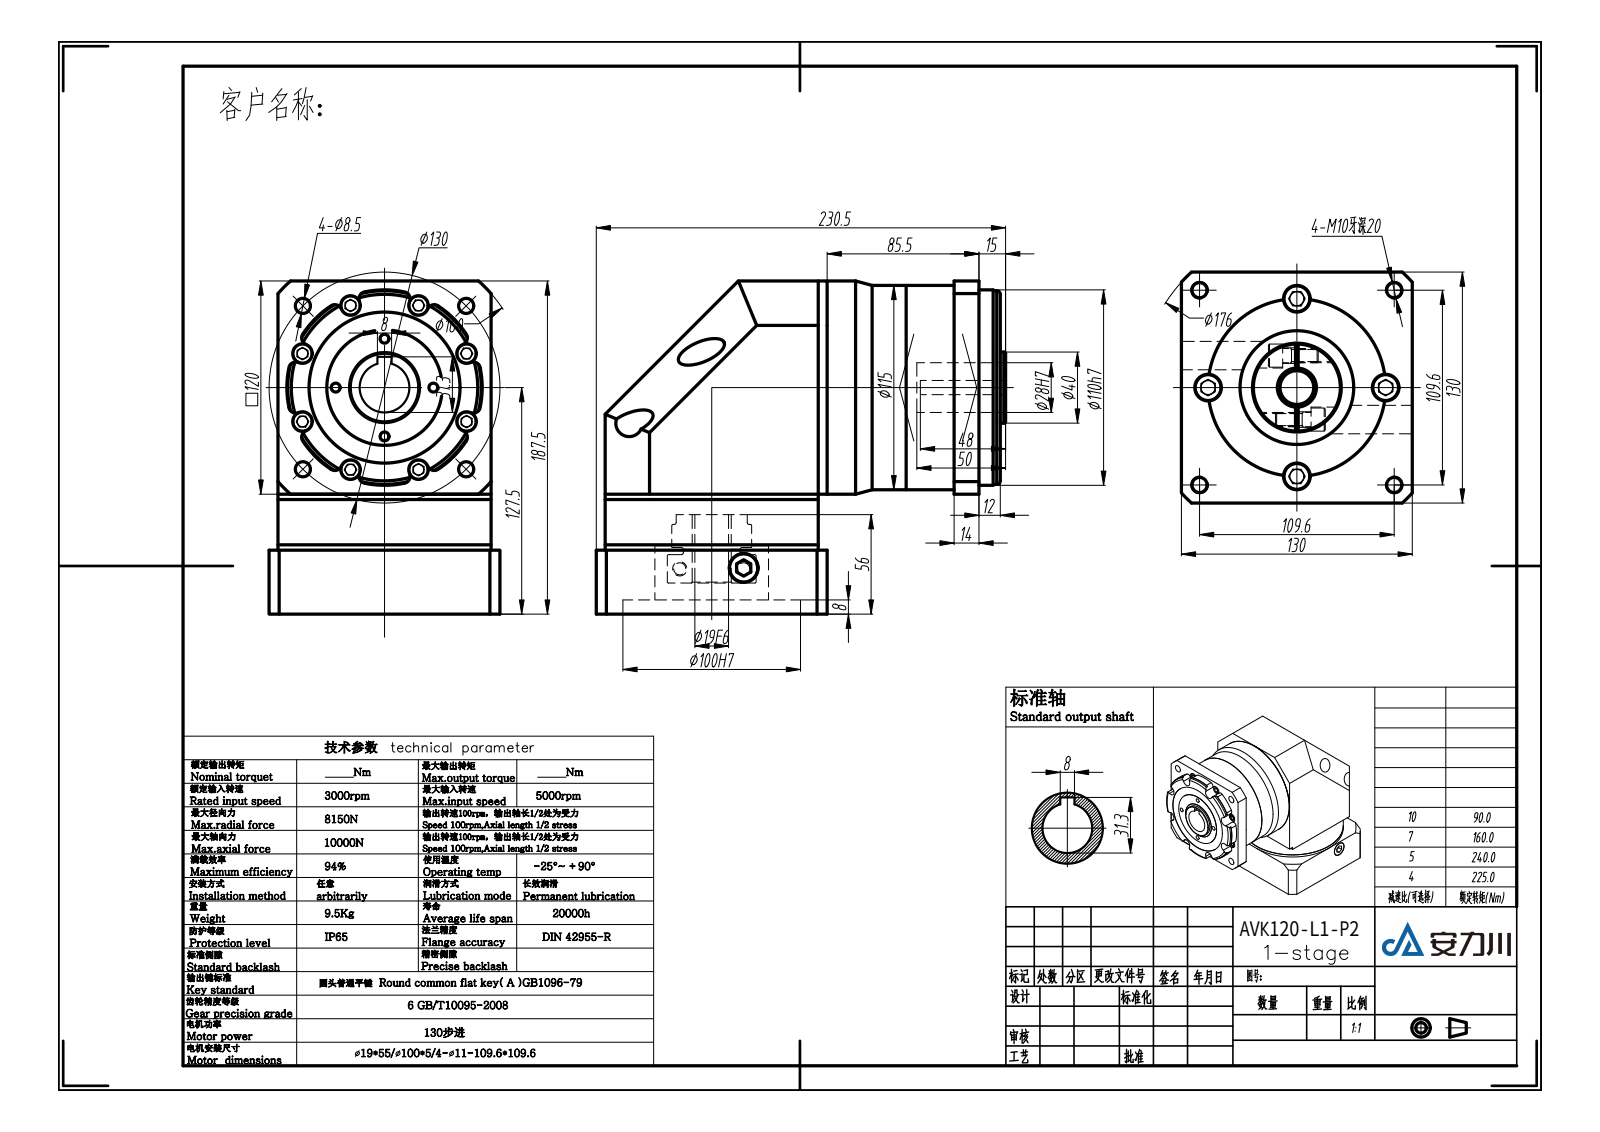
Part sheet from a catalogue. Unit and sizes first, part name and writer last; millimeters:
Units: millimetres
Overall size (bounding box): 230.5 × 187.5 × 130
Round holes (diameter × count): ⌀15 ×10, ⌀8.5 ×8, ⌀11 ×8, ⌀5 ×4, ⌀16 ×2, ⌀19 ×1, ⌀20 ×1, ⌀22 ×1, ⌀28 ×1, ⌀45.2 ×1, ⌀70 ×1, ⌀85 ×1
Round bosses / shafts (diameter × count): ⌀13 ×10, ⌀9.5 ×8, ⌀120 ×2, ⌀15.6 ×2, ⌀115 ×1, ⌀65 ×1, ⌀50 ×1, ⌀45 ×1
Partial cylindrical surfaces — rounded edges, fillets, slot ends (radius × count): R4 ×16, R54.5 ×1, R55 ×1, R80 ×1, R88 ×1
Main face-to-face distances: 5, 25.5, 19.17, 44.5, 49.5, 25.33, 30.33, 120, 125, 3
Hole centre spacings: 39.29, 94.69, 26.74, 26.83, 46.94, 49.53, 49.99, 55.01
Volume: 3 111 000 mm³ · Surface area: 346 455 mm²
Bodies: 23 solids, 503 faces (276 planar, 202 cylindrical, 25 other)
Part name (STEP PRODUCT): VGZK115单级模型（19-55 100-5 4-11-109.6-109.6）
STEP written by: SolidWorks 2016 (AUTOMOTIVE_DESIGN)
